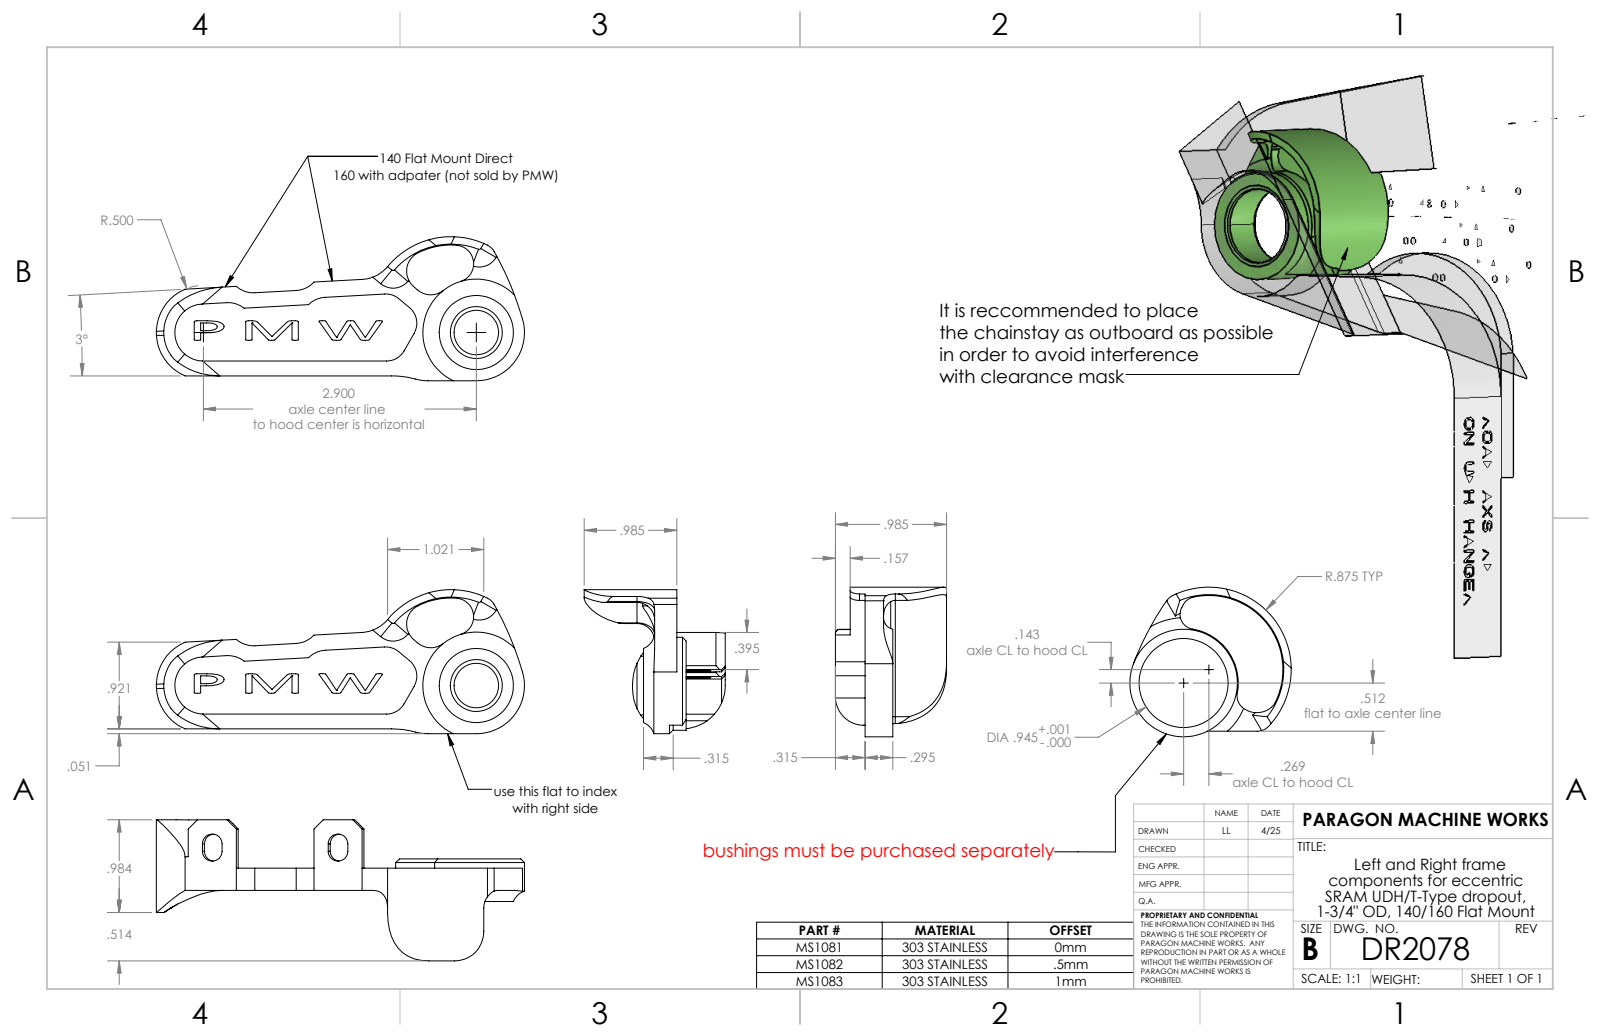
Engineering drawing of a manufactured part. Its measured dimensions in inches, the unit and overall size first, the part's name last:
Units: inches
Overall size (bounding box): 3.912 × 1.53 × 1.498
Round holes (diameter × count): ⌀0.472 ×1
Partial cylindrical surfaces — rounded edges, fillets, slot ends (radius × count): R0.217 ×6, R0.104 ×4, R0.187 ×4, R0.276 ×4, R0.394 ×4, R0.512 ×4, R0.02 ×2, R0.197 ×2
Main face-to-face distances: 0.079, 0.157, 0.236, 0.039, 0.197, 0.118, 0.098, 0.393, 0.315, 0.138
Volume: 1.031 in³ · Surface area: 17.23 in²
Bodies: 1 solid, 190 faces (91 planar, 56 cylindrical, 43 other)
Part name (STEP PRODUCT): DR2076
STEP written by: SolidWorks 2023 (AUTOMOTIVE_DESIGN)
